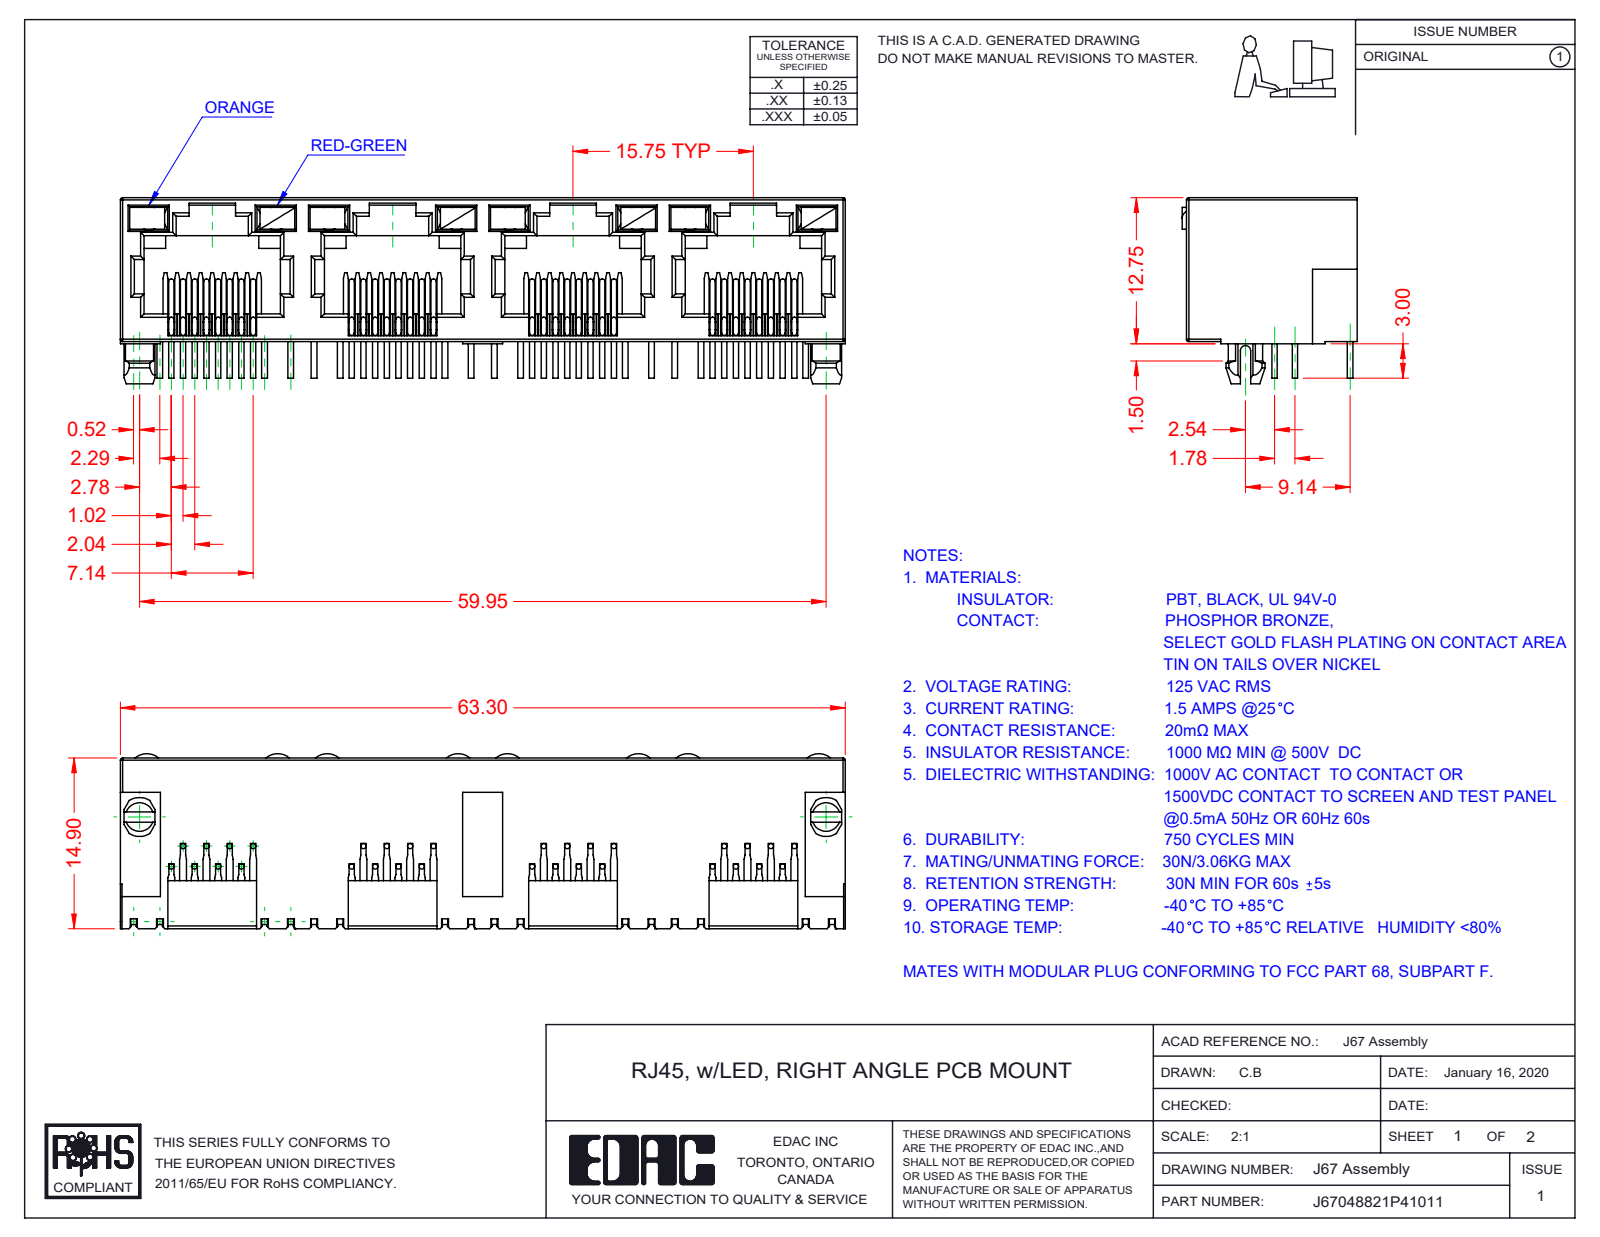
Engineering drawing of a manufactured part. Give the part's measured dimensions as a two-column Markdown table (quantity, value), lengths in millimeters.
| quantity | value |
| --- | --- |
| part name | 67 Insulator; 67 LED LH_4-Orange; J67048822P46011; 67 LED RH_6-Red-Green (+1 more) |
| STEP written by | SolidWorks 2016 (CONFIG_CONTROL_DESIGN) |
| units | millimeters |
| bodies | 41 solids, 2473 faces (1781 planar, 484 cylindrical, 208 other) |
| overall size | 63.3 × 16.25 × 15.28 |
| volume | 5 159 mm³ |
| surface area | 11 573 mm² |
| round bosses / shafts (diameter × count) | 0.46 × 96 |
| partial cylindrical surfaces (radius × count) | 0.2 × 66, 0.3 × 29, 0.45 × 9, 1.55 × 8, 1.5 × 2, 1.7 × 2, 0.35 × 1, 1 × 1 |
| main face-to-face distances | 0.5, 12.55, 1.89, 0.89, 10, 15.75, 1, 1.39, 11, 11.89 |
